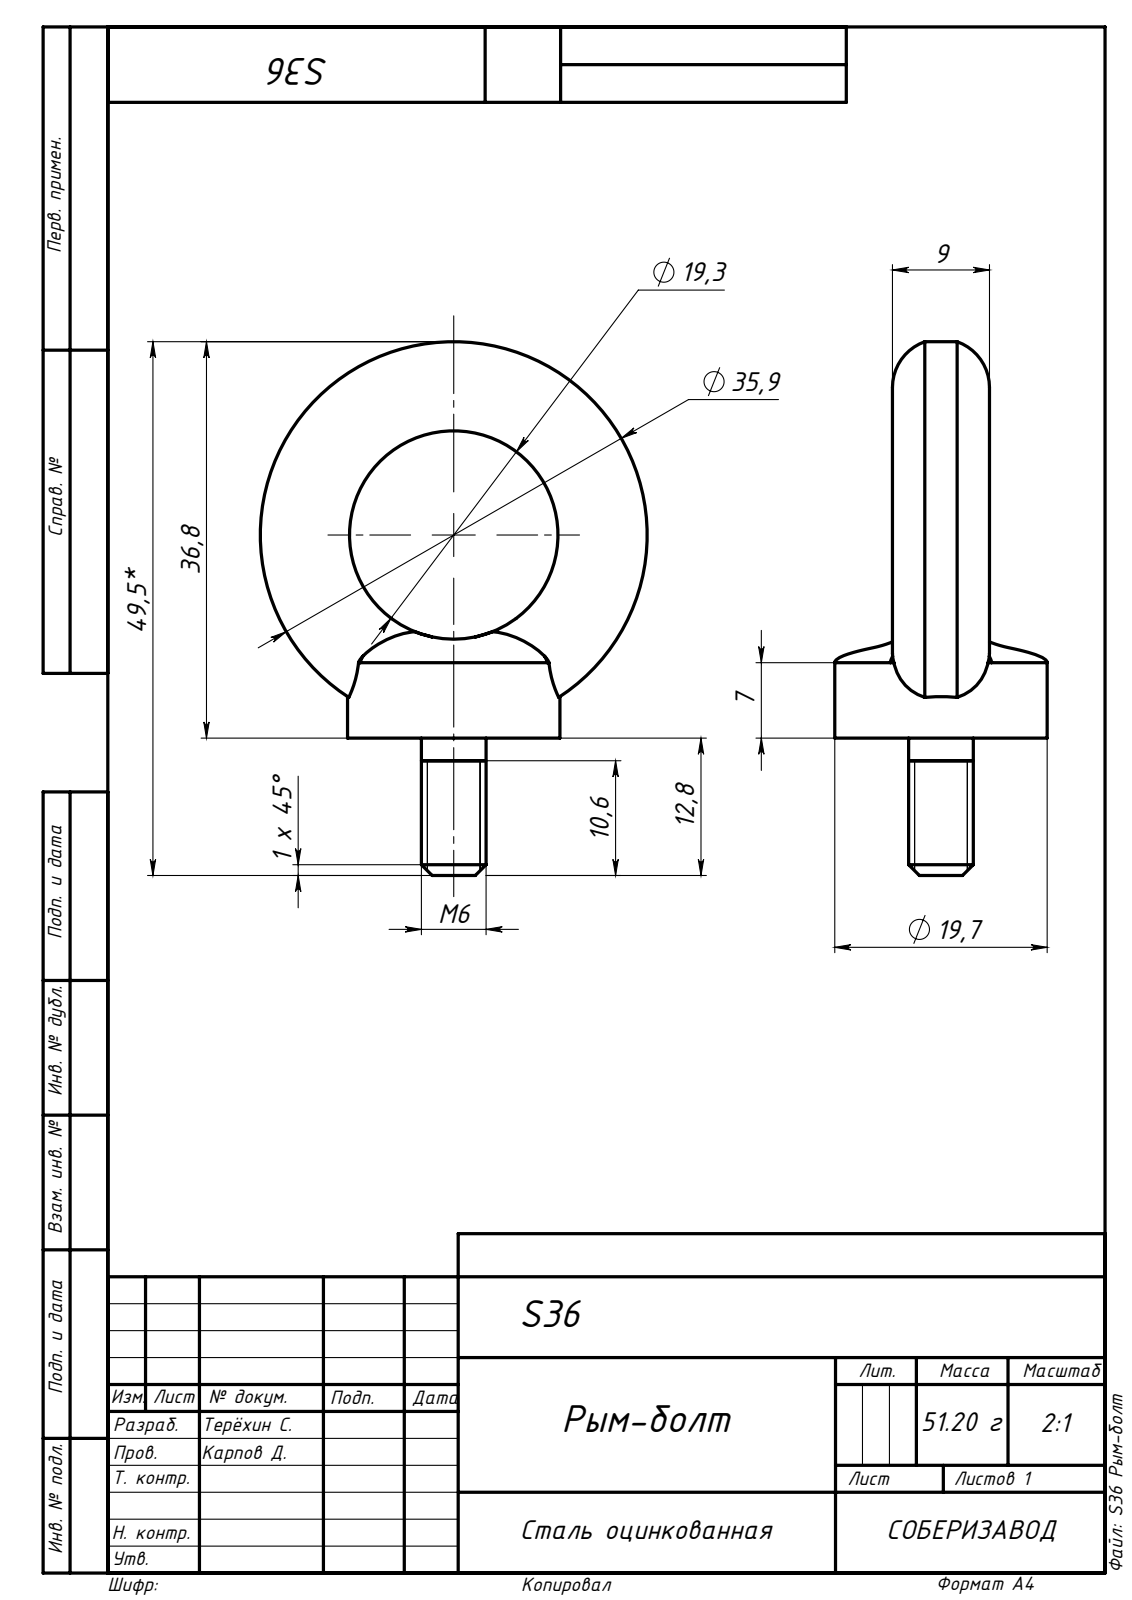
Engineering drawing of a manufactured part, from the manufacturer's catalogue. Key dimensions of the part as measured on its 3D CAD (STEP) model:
Part name (STEP PRODUCT): S36 Рым-болт
STEP written by: SolidWorks 2020 (AUTOMOTIVE_DESIGN)
Units: millimetres
Bodies: 1 solid, 25 faces (2 planar, 9 cylindrical, 14 other)
Overall size (bounding box): 49.54 × 35.88 × 19.7
Volume: 7 258 mm³ · Surface area: 3 152 mm²
Round holes (diameter × count): ⌀19.34 ×1
Round bosses / shafts (diameter × count): ⌀35.89 ×1, ⌀19.7 ×1, ⌀6 ×1
Main face-to-face distances: 12.75
